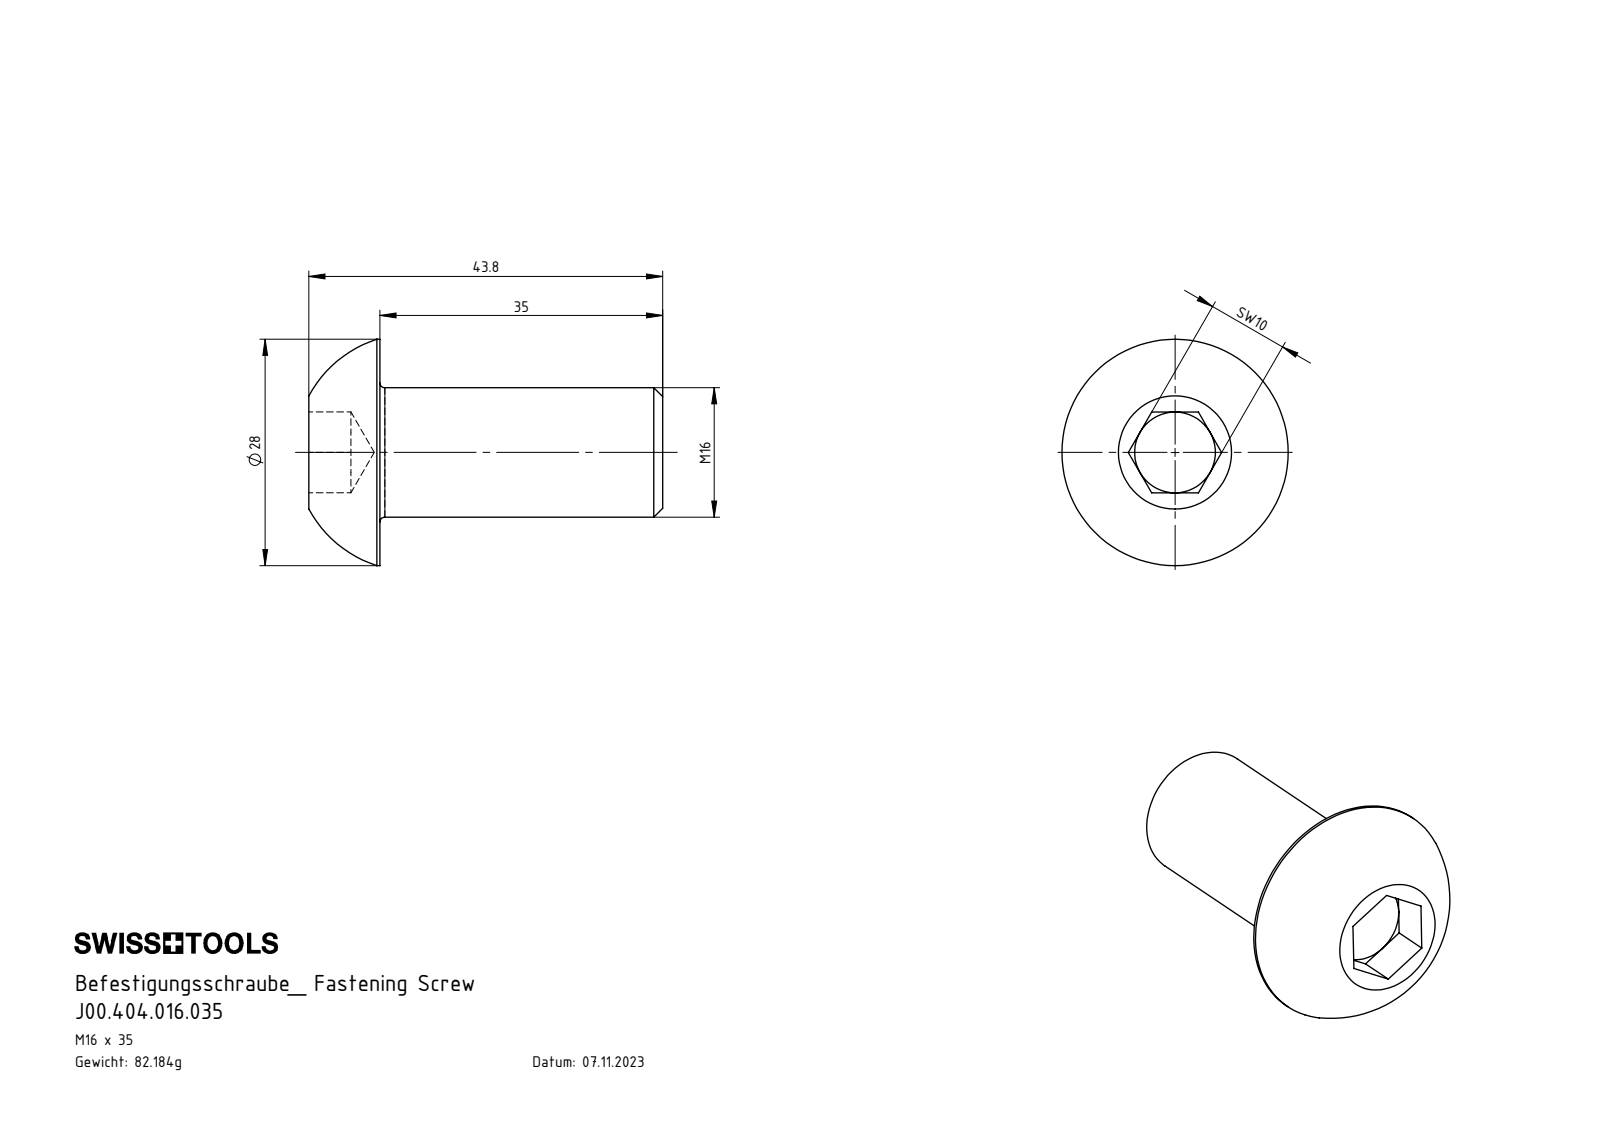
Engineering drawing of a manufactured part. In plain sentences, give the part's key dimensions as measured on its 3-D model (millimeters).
The part is named "J00.404.016.035". Its 3-D file was written by "SolidWorks 2022 (AUTOMOTIVE_DESIGN)". It is 1 solid with 27 faces: 15 planar, 4 cylindrical and 8 other. Overall it measures 43.8 by 28 by 28 millimeters. Its volume is 10 273 cubic millimeters and its surface area 3 486 square millimeters. Round bosses or shafts: 1 of diameter 28, 1 of diameter 16. The main face-to-face distances are 35, 10, 8.8, 43.8, 5.2, 3.6, 38.6.
